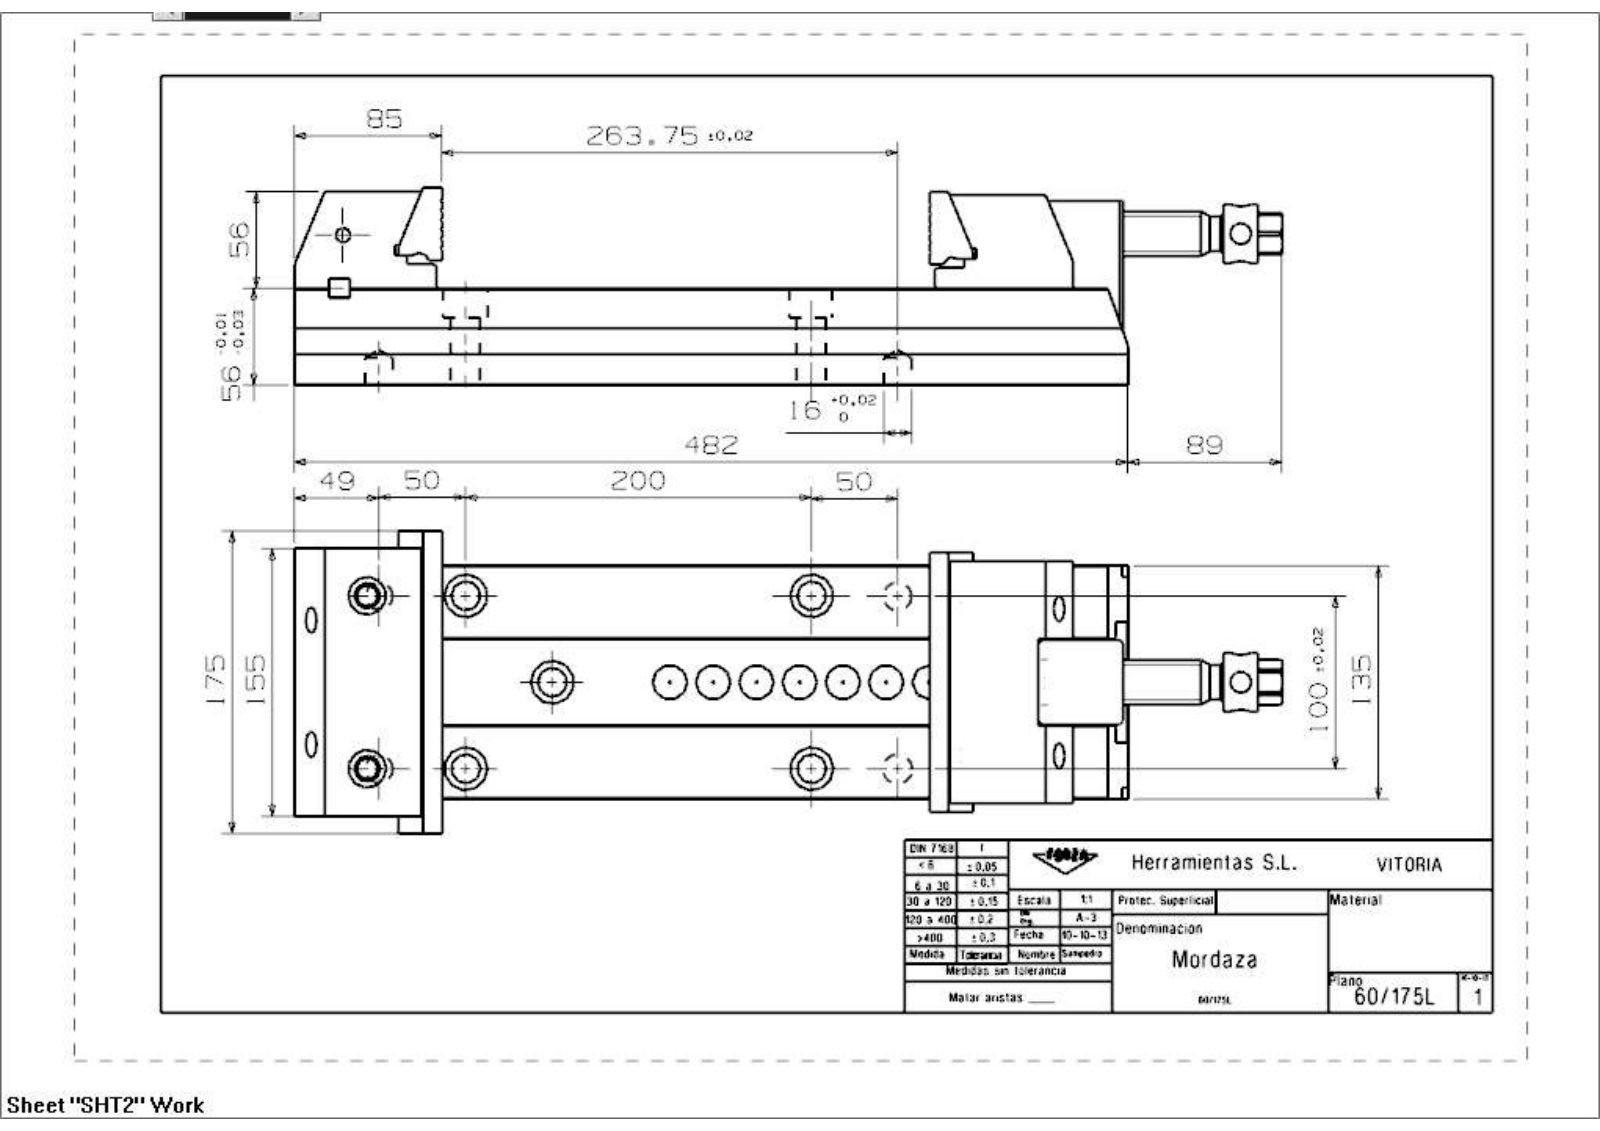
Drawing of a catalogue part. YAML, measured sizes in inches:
part_name: "3015002 Husillo; 3015011 Tuerca de bronce; 3015008 Bulon; 3015007 Taco husillo (+6 more)"
step_written_by: "SIEMENS PLM Software NX 7.5 (CONFIG_CONTROL_DESIGN)"
units: inches
bodies: {solids: 12, faces: 449, planar: 286, cylindrical: 96, other: 67}
overall_size: [22.48, 6.89, 4.5]
volume: 238.1
surface_area: 808.5
round_holes:
  - {diameter: 0.591, count: 6}
  - {diameter: 0.63, count: 5}
  - {diameter: 0.669, count: 5}
  - {diameter: 0.984, count: 5}
  - {diameter: 0.275, count: 4}
  - {diameter: 0.335, count: 4}
  - {diameter: 0.346, count: 4}
  - {diameter: 0.394, count: 4}
  - {diameter: 0.417, count: 4}
  - {diameter: 0.512, count: 4}
  - {diameter: 0.748, count: 4}
  - {diameter: 0.472, count: 2}
round_bosses_or_shafts:
  - {diameter: 1.339, count: 1}
  - {diameter: 1.331, count: 1}
  - {diameter: 1.024, count: 1}
  - {diameter: 0.787, count: 1}
  - {diameter: 0.65, count: 1}
partial_cylinders:
  - {radius: 0.787, count: 4}
  - {radius: 0.063, count: 2}
  - {radius: 0.236, count: 2}
  - {radius: 0.276, count: 2}
  - {radius: 0.157, count: 1}
  - {radius: 0.354, count: 1}
  - {radius: 0.413, count: 1}
  - {radius: 0.492, count: 1}
face_to_face_distances: [2.205, 1.252, 0.953, 4.035, 5.315, 0.394, 1.28, 1.673, 1.024, 3.622]
hole_center_spacings: [3.092, 3.937, 4.402, 0.269, 1.679, 1.969, 2.835, 3.346]
